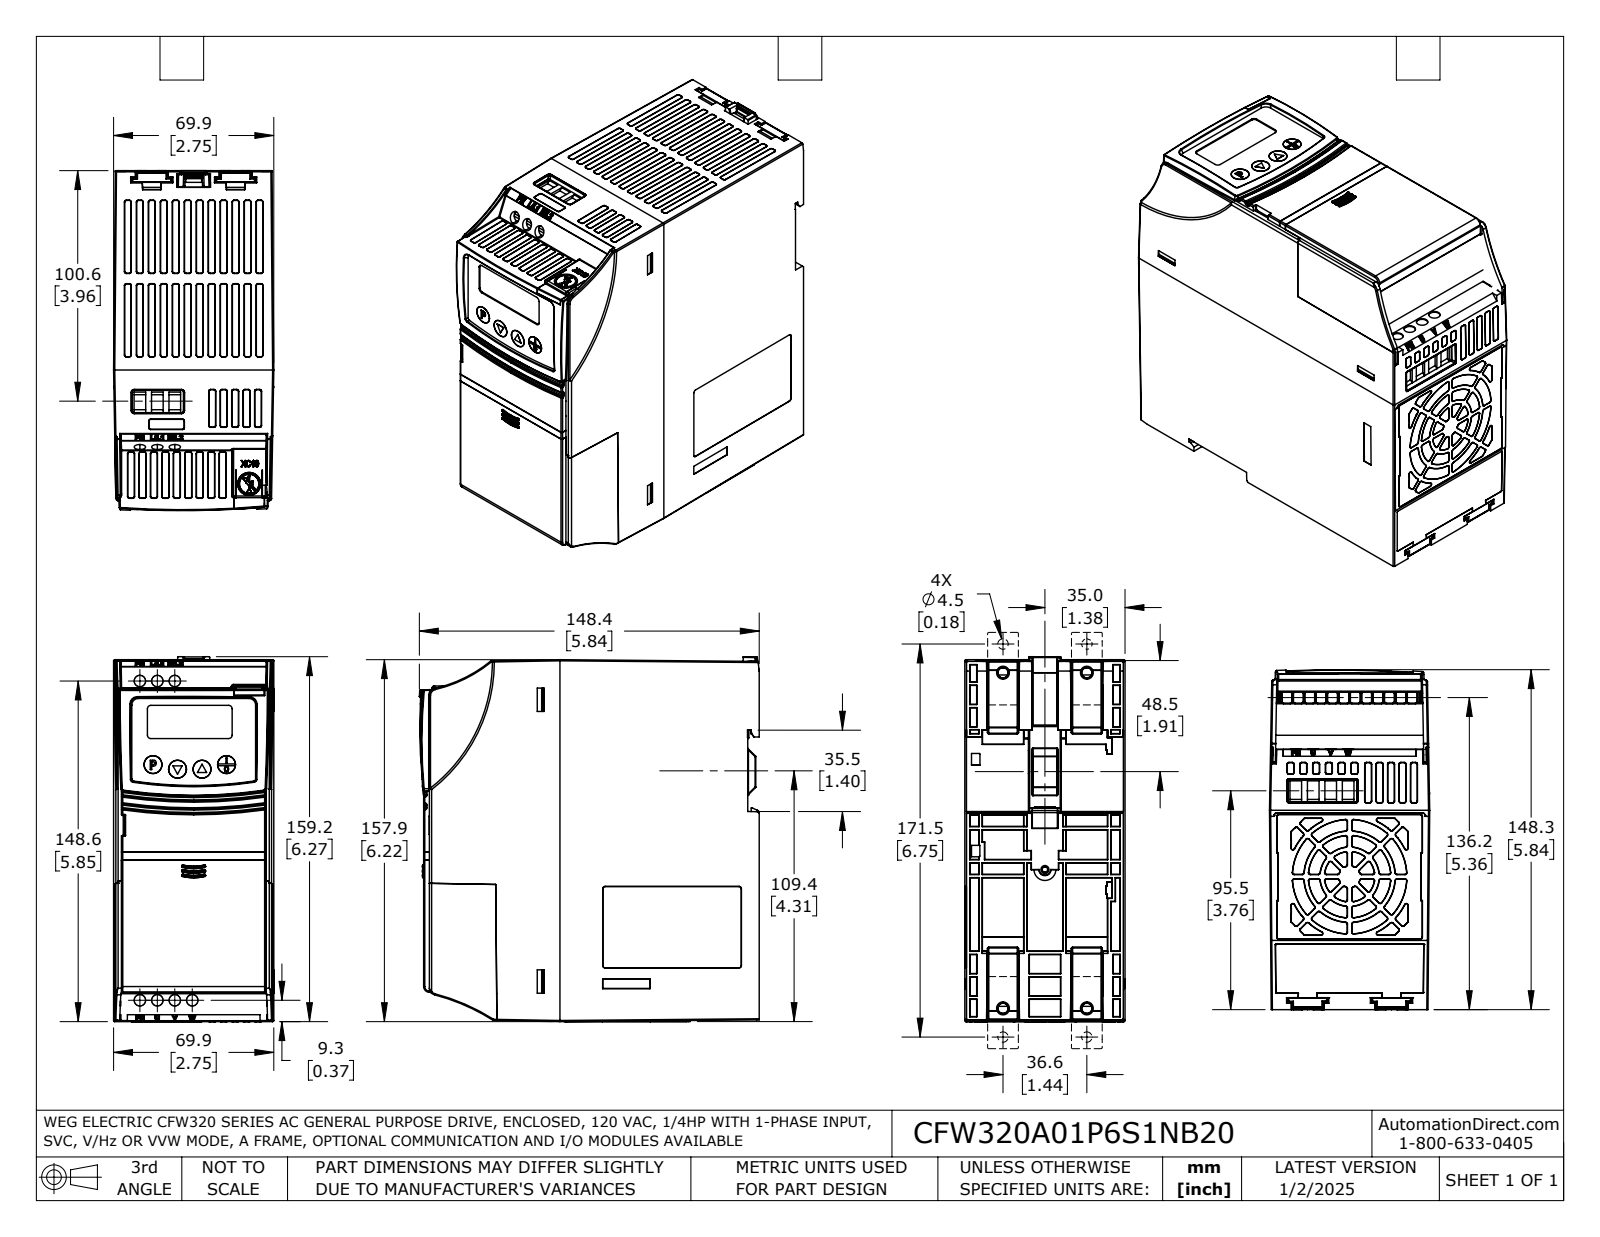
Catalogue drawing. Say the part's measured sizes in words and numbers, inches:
The part is named "CFW320A01P6S1NB20". Its 3-D file was written by "SolidWorks 2021 (AUTOMOTIVE_DESIGN)". It is 6 solids with 3715 faces: 1587 planar, 853 cylindrical and 1275 other. Overall it measures 6.269 by 5.841 by 2.754 inches. Its volume is 15.24 cubic inches and its surface area 309 square inches. Round holes: 3 of diameter 0.197. Partial cylindrical surfaces (rounded edges, fillets, slot ends): 327 of radius 0.012, 150 of radius 0.02, 13 of radius 0.039, 5 of radius 0.03, 3 of radius 0.118, 2 of radius 0.01, 1 of radius 0.098, 1 of radius 0.126. The main face-to-face distances are 0.07, 0.055, 0.019, 0.05, 6, 5.33, 5.275, 5.571, 5.516, 0.241. The hole center spacings are 0.3, 0.6.
